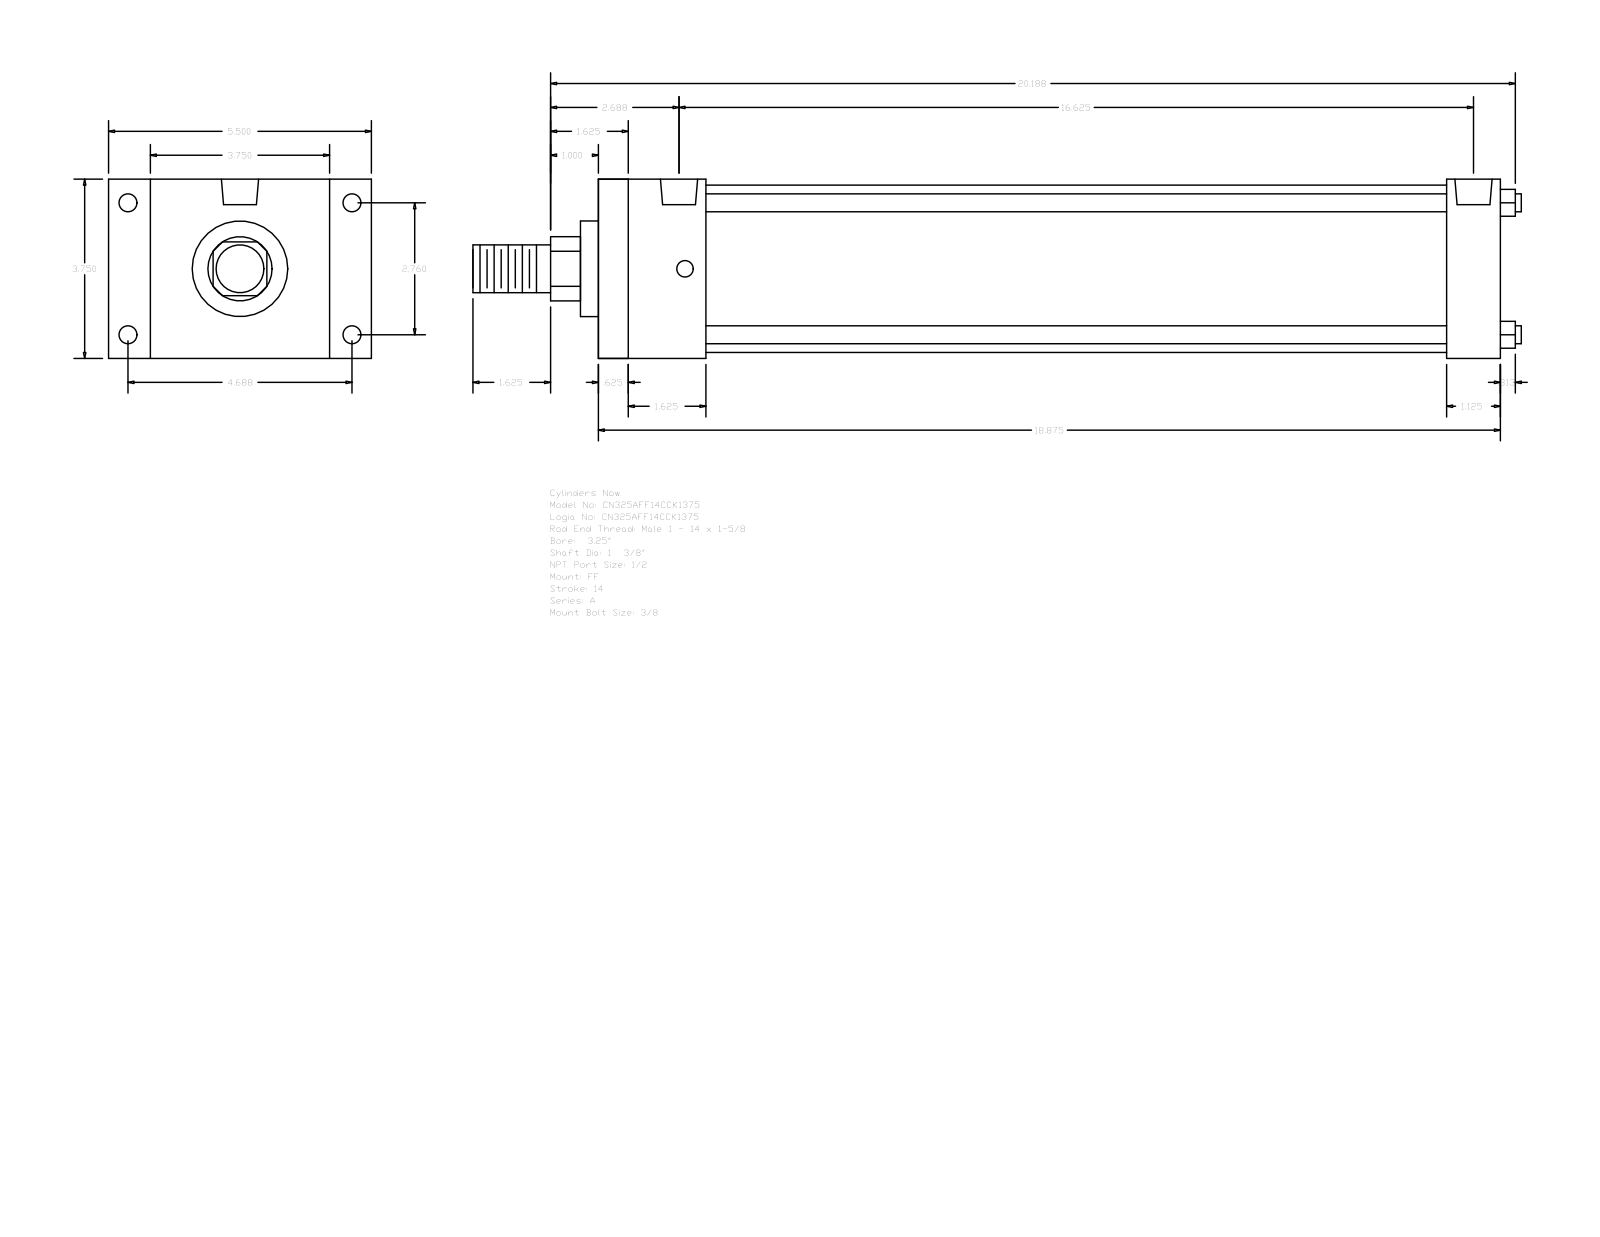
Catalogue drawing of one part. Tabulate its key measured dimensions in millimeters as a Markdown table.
| quantity | value |
| --- | --- |
| part name | A_FF__0325_1.375 |
| STEP written by | GSSL Pune (CONFIG_CONTROL_DESIGN) |
| units | millimeters |
| bodies | 0 solids, 92 faces (64 planar, 28 cylindrical, 0 other) |
| overall size | 557.21 × 139.7 × 95.25 |
| round holes (diameter × count) | 8.73 × 4, 9.53 × 4, 19.77 × 2 |
| round bosses / shafts (diameter × count) | 9.53 × 4, 88.9 × 1, 50.8 × 1, 34.92 × 1, 25.4 × 1 |
| partial cylindrical surfaces (radius × count) | 17.06 × 1 |
| main face-to-face distances | 95.24, 479.42, 463.55, 15.87, 57.15, 22.23, 117.47, 28.57, 450.85, 41.28 |
| hole center spacings | 3.18, 70.1, 119.06, 138.16, 415.92, 419.1, 422.28 |
